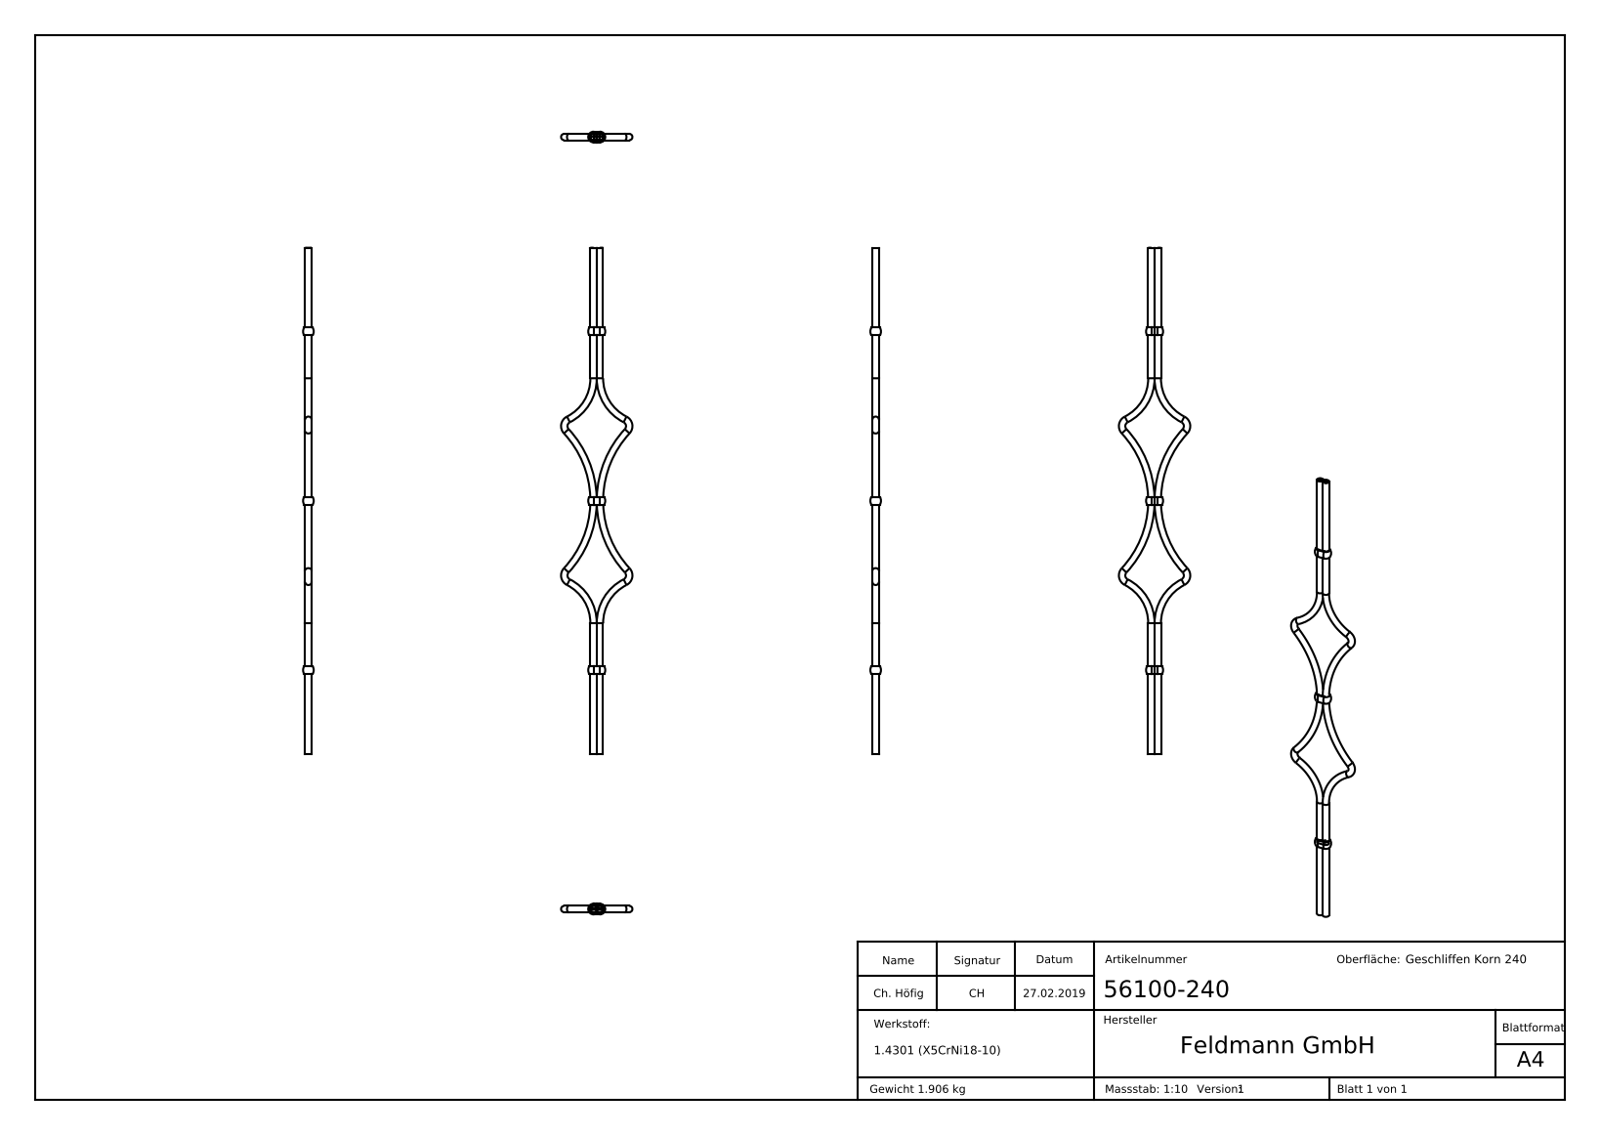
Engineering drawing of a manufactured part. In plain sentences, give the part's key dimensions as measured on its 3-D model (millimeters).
The part is named "56100-240". Its 3-D file was written by "SolidWorks 2015 (CONFIG_CONTROL_DESIGN)". It is 5 solids with 321 faces: 160 planar, 25 cylindrical and 136 other. Overall it measures 950 by 133.99 by 20 millimeters. Its volume is 241 318 cubic millimeters and its surface area 84 644 square millimeters. Round holes: 2 of diameter 12. Partial cylindrical surfaces (rounded edges, fillets, slot ends): 6 of radius 14.14. The main face-to-face distances are 317.75, 12, 14.5, 467.75, 482.25, 164.5, 785.5, 303.25, 150, 800. The hole center spacings are 12.
